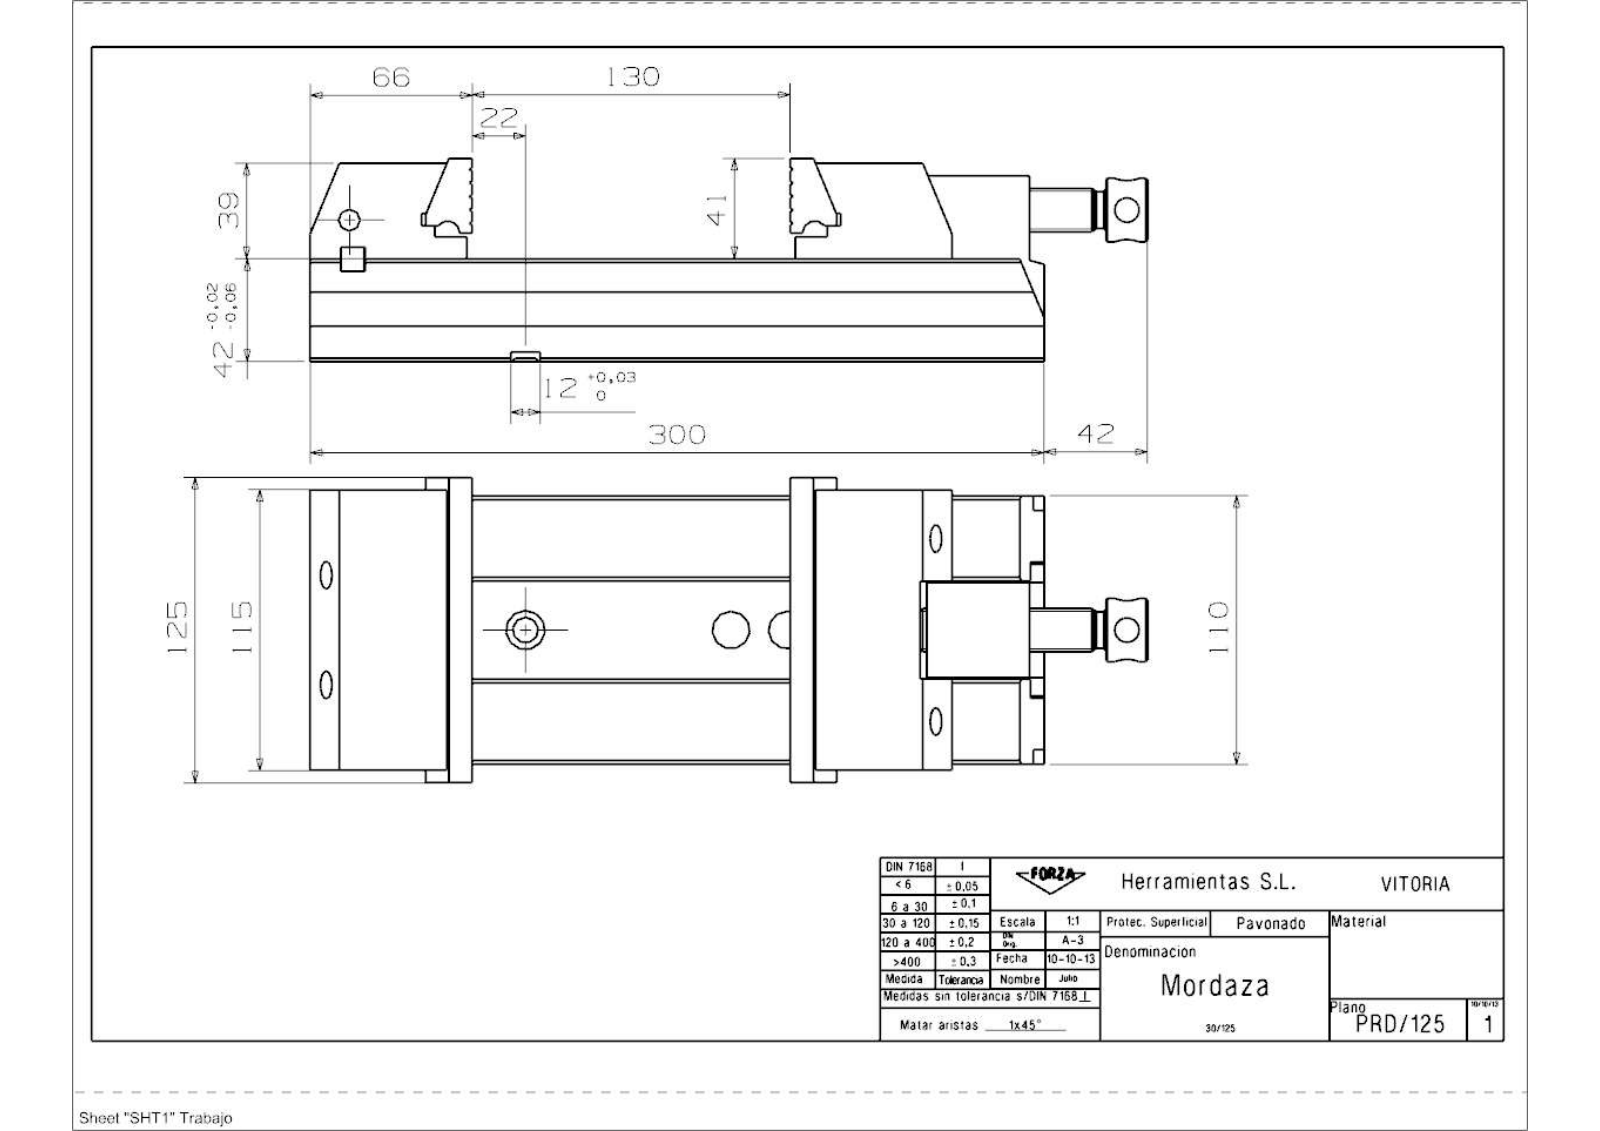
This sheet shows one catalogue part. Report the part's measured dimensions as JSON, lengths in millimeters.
{"part_name": "PRD_125_Mordaza", "step_written_by": "SIEMENS PLM Software NX 9.0 (CONFIG_CONTROL_DESIGN)", "units": "millimeters", "bodies": {"solids": 11, "faces": 426, "planar": 268, "cylindrical": 116, "other": 42}, "overall_size": [342.31, 125, 83], "volume_mm3": 1568000, "surface_area_mm2": 272333, "round_holes": [[4.35, 5], [7.5, 4], [11.5, 4], [8.78, 3], [5.19, 2], [6.5, 2], [6.99, 2], [8, 2], [10, 2], [10.5, 2], [11, 2], [12.38, 2]], "round_bosses_or_shafts": [[26, 1], [17.73, 1], [15, 1], [14.5, 1], [10.5, 1]], "partial_cylinders_radius": [[0.3, 20], [6, 7], [10, 4], [16, 4], [1.6, 2], [5, 2], [3, 1], [8, 1]], "face_to_face_distances": [42, 8.5, 15.4, 26.6, 77, 27, 39, 29.5, 2.5, 81], "hole_center_spacings": [60, 9.19, 15, 23.31, 23.76, 25.44, 37.99, 44]}
